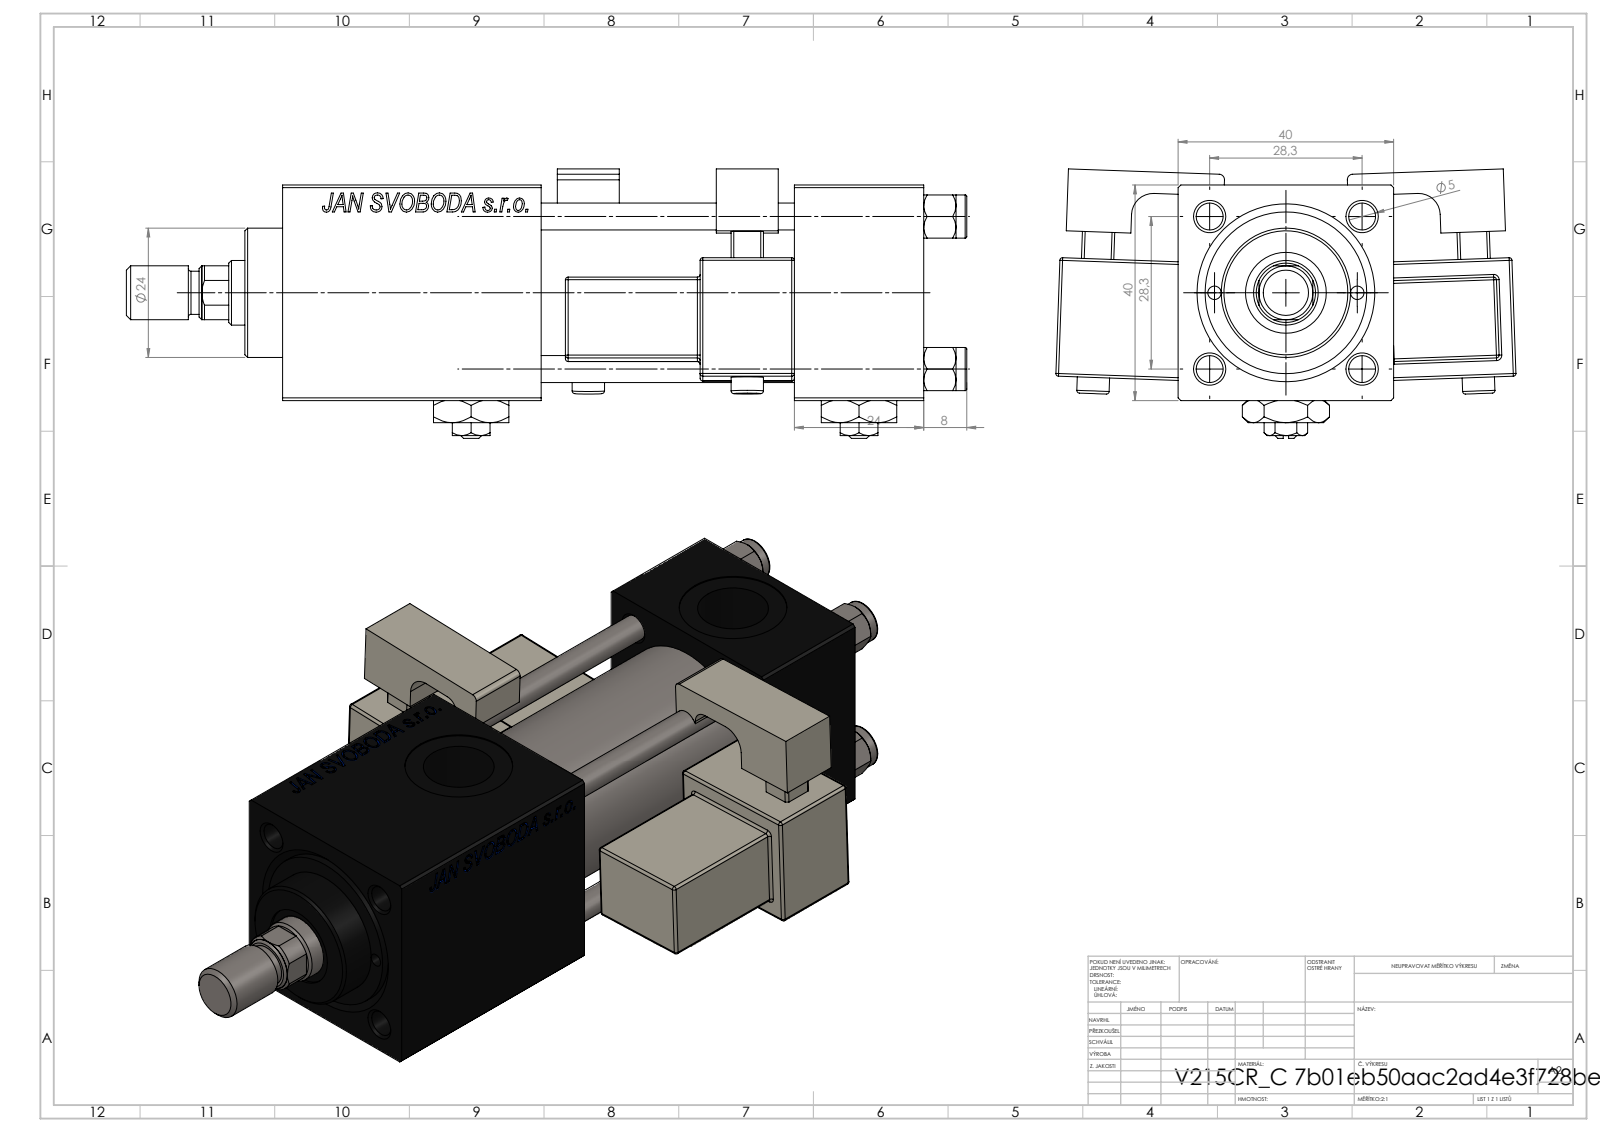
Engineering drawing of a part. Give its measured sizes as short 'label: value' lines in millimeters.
name: V215CR_C_TYCINKA; V215_VC_A; V215CR_VCP_C; V215CR_MSU (+4 more)
written by: SolidWorks 2019 (CONFIG_CONTROL_DESIGN)
unit: mm
bodies: 16 solids, 1426 faces (640 planar, 166 cylindrical, 620 other)
size: 156 × 85.39 × 49.99
volume: 182 131 mm³; area: 68 922 mm²
holes: 4× ⌀5, 3× ⌀20, 2× ⌀2.5, 2× ⌀7, 2× ⌀13.16, 1× ⌀6.5, 1× ⌀12, 1× ⌀15, 1× ⌀25, 1× ⌀30
bosses: 5× ⌀8, 2× ⌀6, 1× ⌀31, 1× ⌀24, 1× ⌀10
rounds: 48× R0.5, 2× R1, 2× R2.5, 2× R4, 1× R5.5
face distances: 40, 20, 24, 3, 47, 71, 39.8, 21.99, 48, 29.5
hole spacings: 14.18, 20.01, 28.3, 30.84, 13.25, 40.02, 26.5, 72
